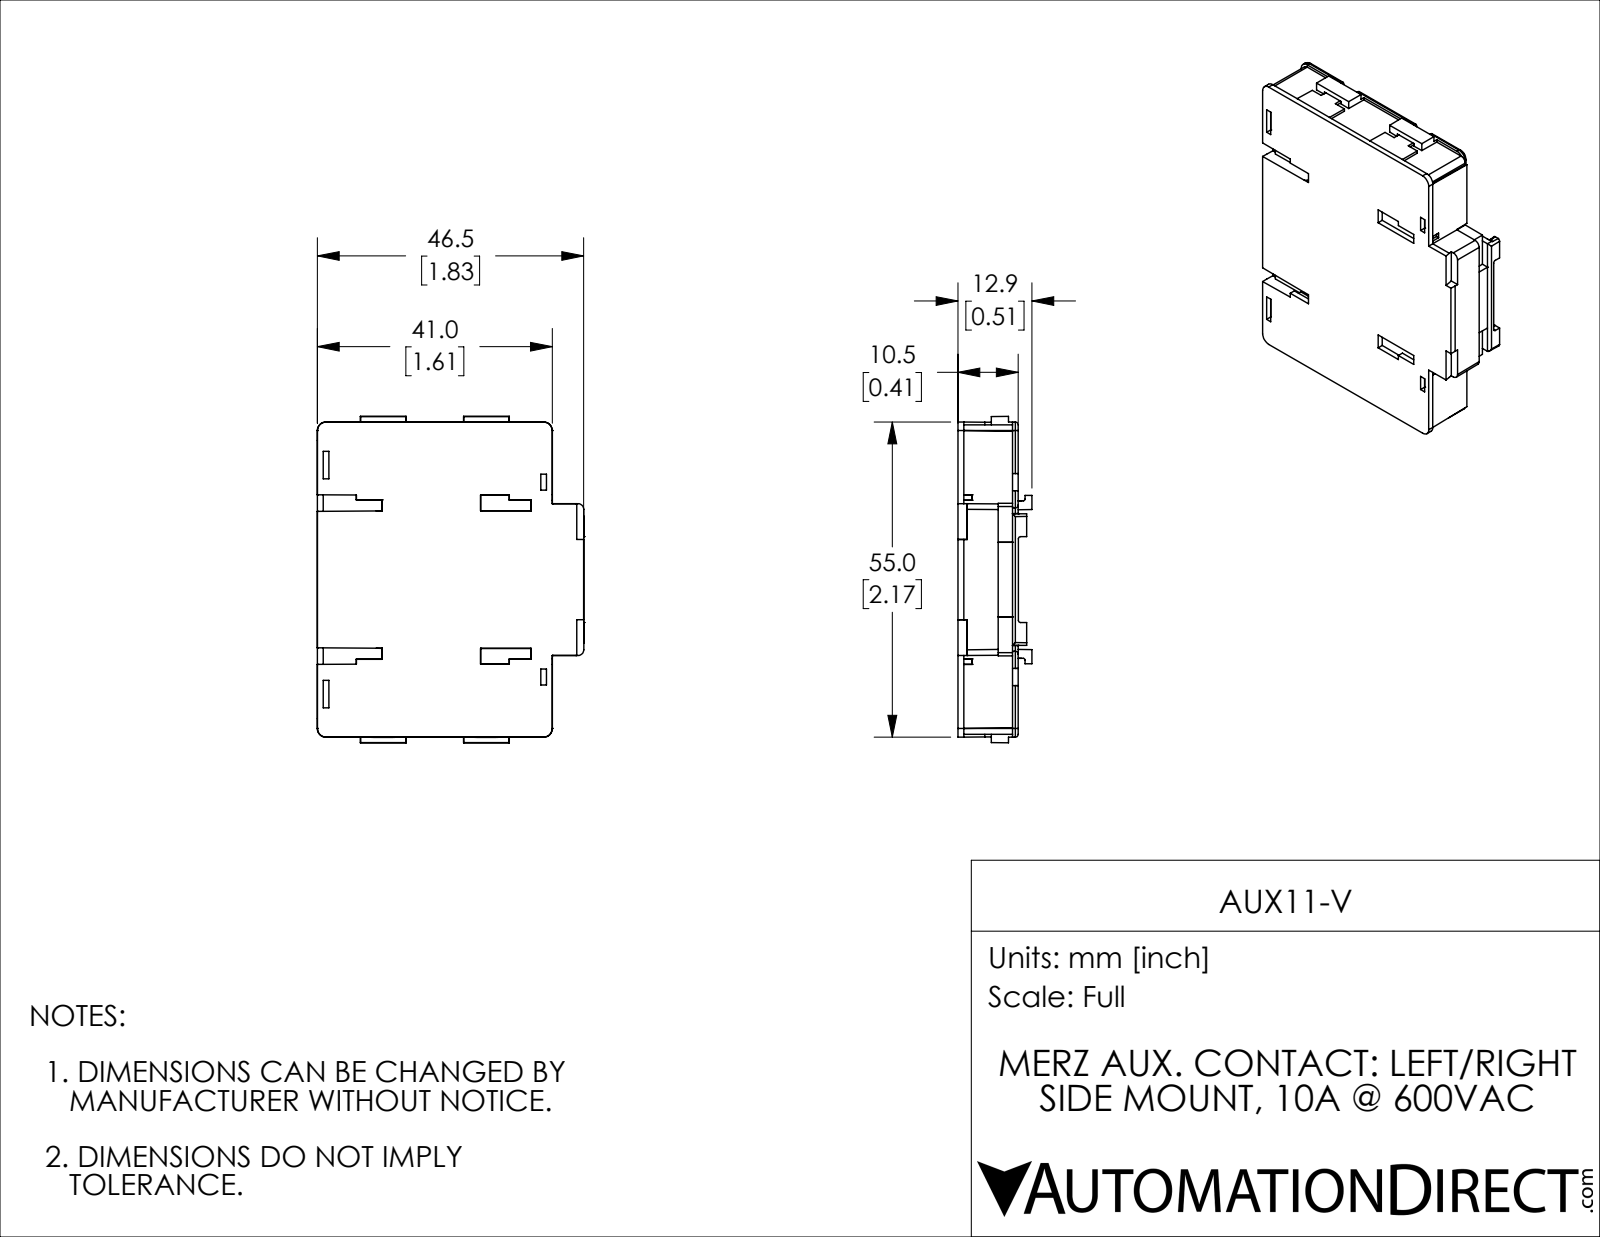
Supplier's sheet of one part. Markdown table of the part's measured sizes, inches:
| quantity | value |
| --- | --- |
| part name | AUX11-V |
| STEP written by | SolidWorks 2019 (AUTOMOTIVE_DESIGN) |
| units | inches |
| bodies | 1 solid, 412 faces (329 planar, 57 cylindrical, 26 other) |
| overall size | 2.243 × 1.832 × 0.508 |
| volume | 1.501 in³ |
| surface area | 12.22 in² |
| partial cylindrical surfaces (radius × count) | 0.02 × 14, 0.016 × 7, 0.039 × 6, 0.012 × 4, 0.031 × 2 |
| main face-to-face distances | 0.413, 0.039, 0.374, 2.126, 0.217, 0.036, 1.792, 2.202, 0.146, 0.335 |
